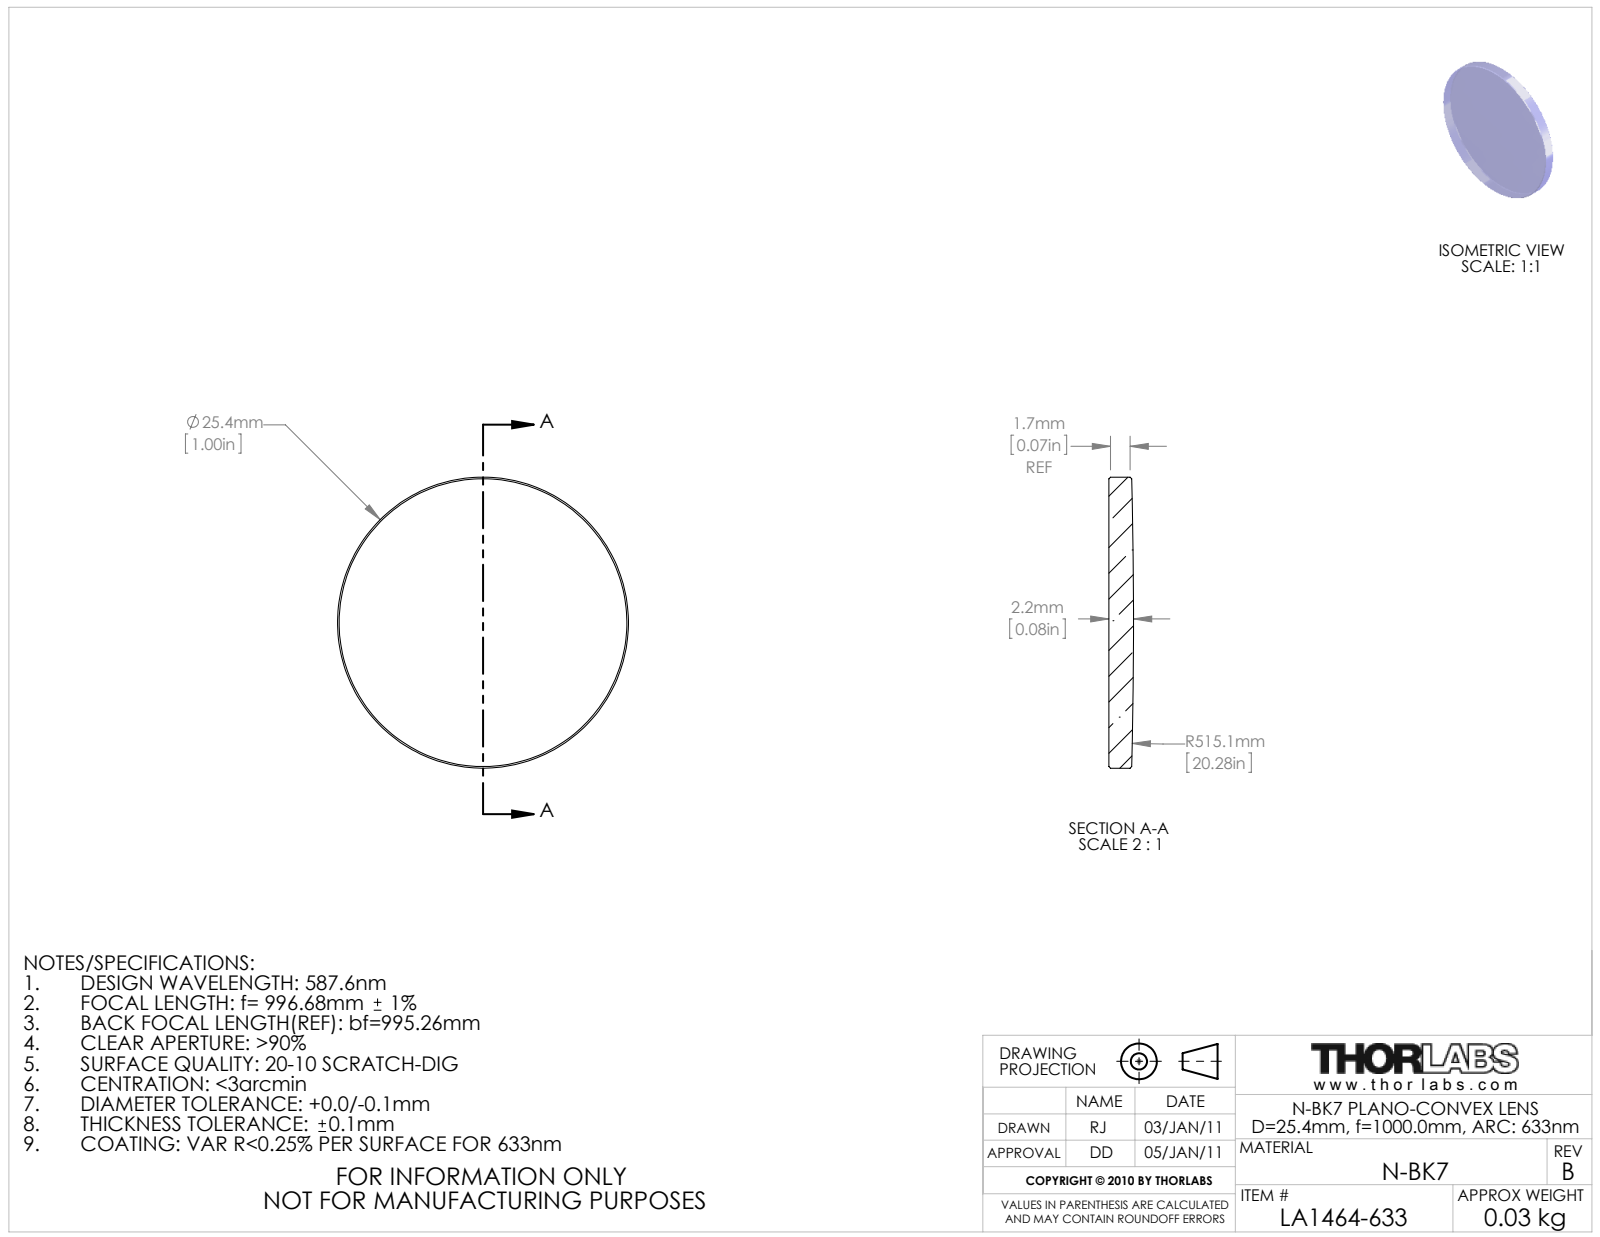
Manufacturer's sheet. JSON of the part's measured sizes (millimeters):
{"part_name": "21807-E0W", "step_written_by": "SolidWorks 2011 (AUTOMOTIVE_DESIGN)", "units": "millimeters", "bodies": {"solids": 0, "faces": 9, "planar": 1, "cylindrical": 2, "other": 6}, "overall_size": [25.4, 25.4, 2.15], "round_bosses_or_shafts": [[25.4, 1]]}
